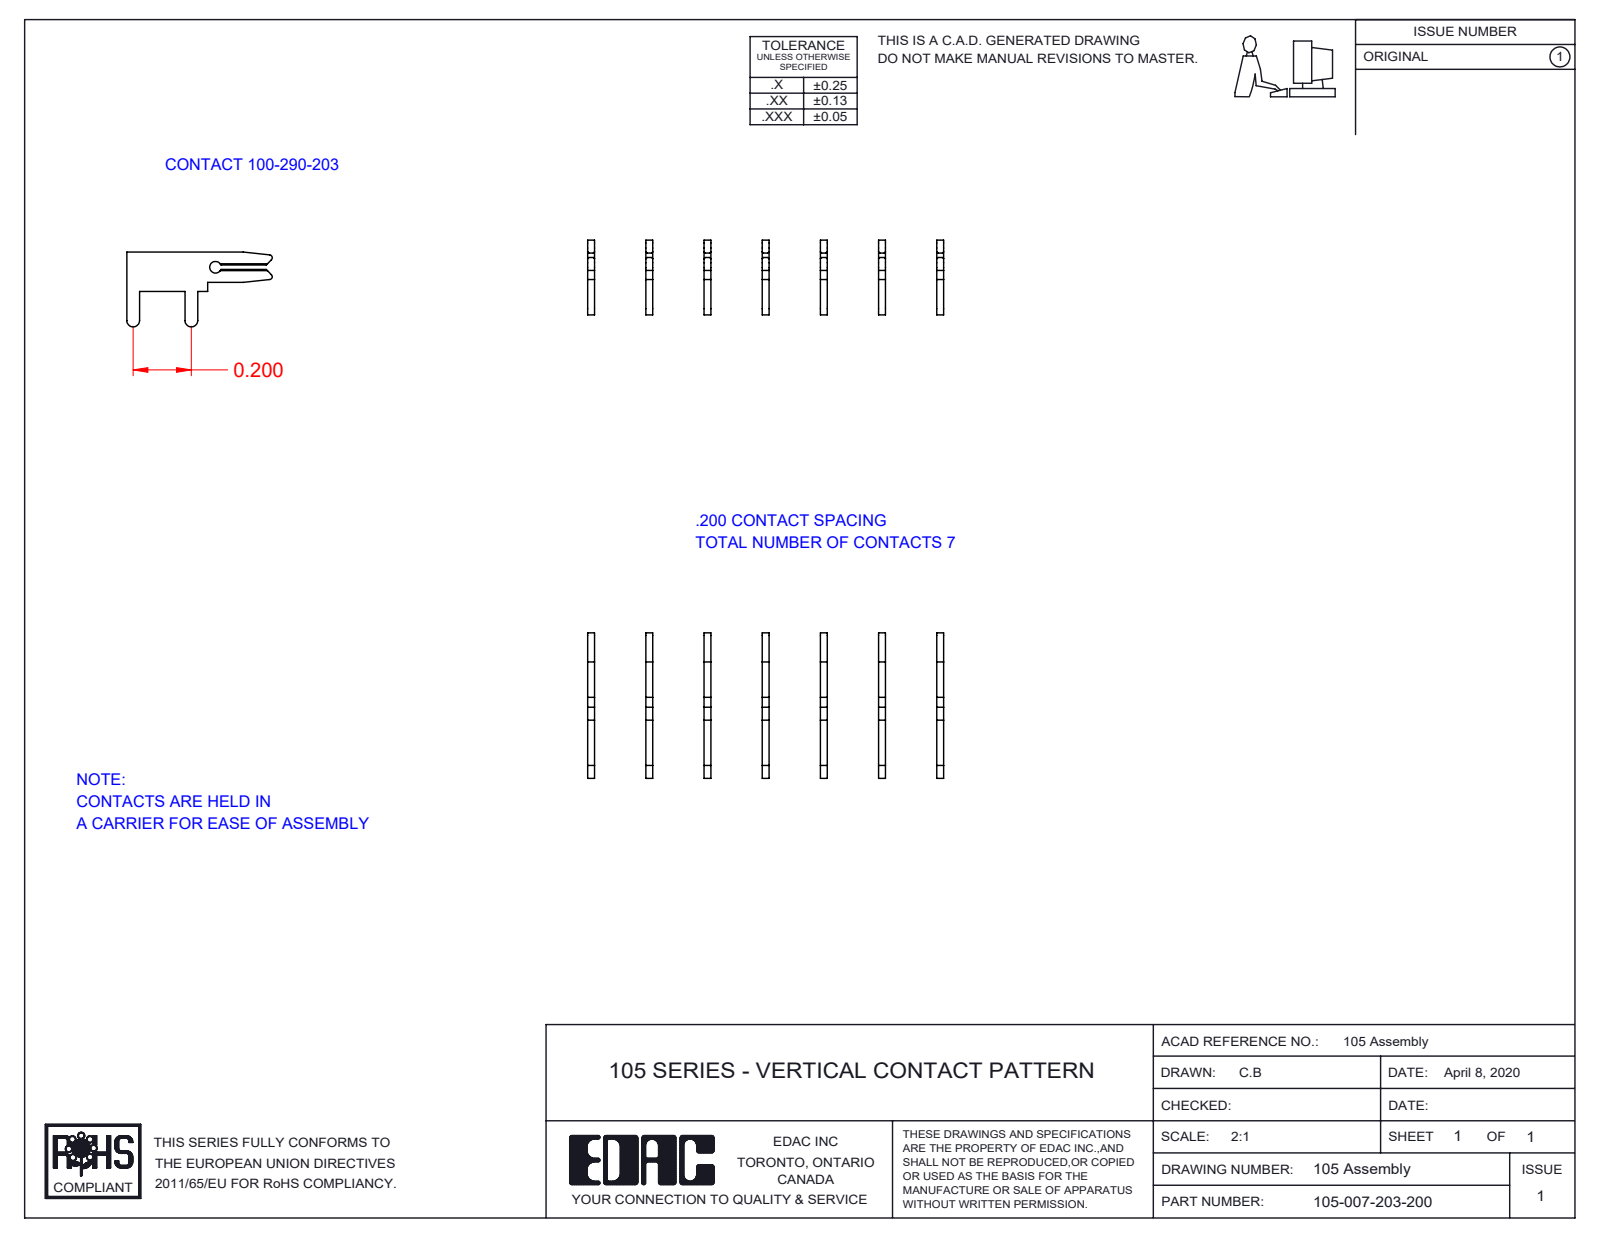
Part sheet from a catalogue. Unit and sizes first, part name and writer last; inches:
Units: inches
Overall size (bounding box): 1.224 × 0.5 × 0.257
Round holes (diameter × count): ⌀0.04 ×1
Partial cylindrical surfaces — rounded edges, fillets, slot ends (radius × count): R0.01 ×2, R0.022 ×2
Main face-to-face distances: 0.2, 0.4, 0.6, 0.024, 0.8, 0.224, 0.176, 0.424, 0.376, 1
Volume: 0.011 in³ · Surface area: 1.256 in²
Bodies: 7 solids, 196 faces (147 planar, 49 cylindrical, 0 other)
Part name (STEP PRODUCT): 105-007-203-200; 100-290-001_100-290-203
STEP written by: SolidWorks 2020 (CONFIG_CONTROL_DESIGN)
